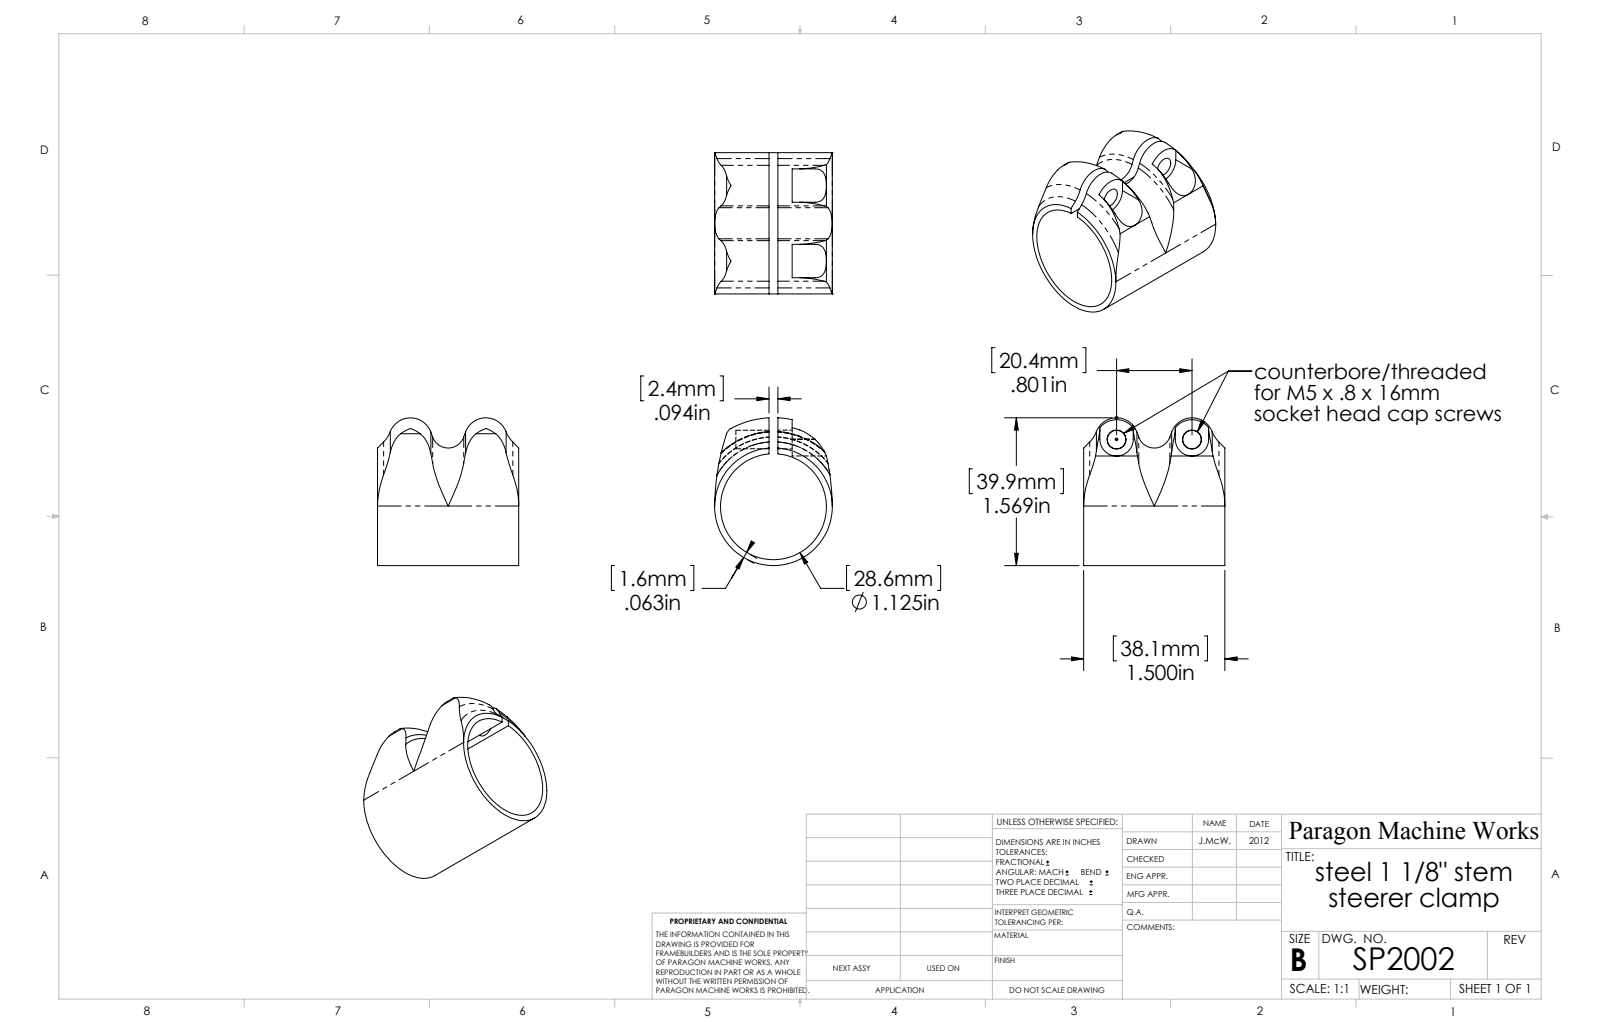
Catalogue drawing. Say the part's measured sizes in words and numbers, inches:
The part is named "SP2002". Its 3-D file was written by "SolidWorks 2012 (AUTOMOTIVE_DESIGN)". It is 1 solid with 48 faces: 12 planar, 18 cylindrical and 18 other. Overall it measures 1.569 by 1.5 by 1.25 inches. Its volume is 0.594 cubic inches and its surface area 14.21 square inches. Round holes: 2 of diameter 0.197, 2 of diameter 0.2, 1 of diameter 1.125. Partial cylindrical surfaces (rounded edges, fillets, slot ends): 2 of radius 0.177, 2 of radius 2.554, 1 of radius 0.1, 1 of radius 0.5, 1 of radius 0.625. The main face-to-face distances are 0.094, 1.5, 0.245, 0.151, 0.353, 0.447, 0.598, 0.172, 1.328, 0.526. The hole center spacings are 0.802.
